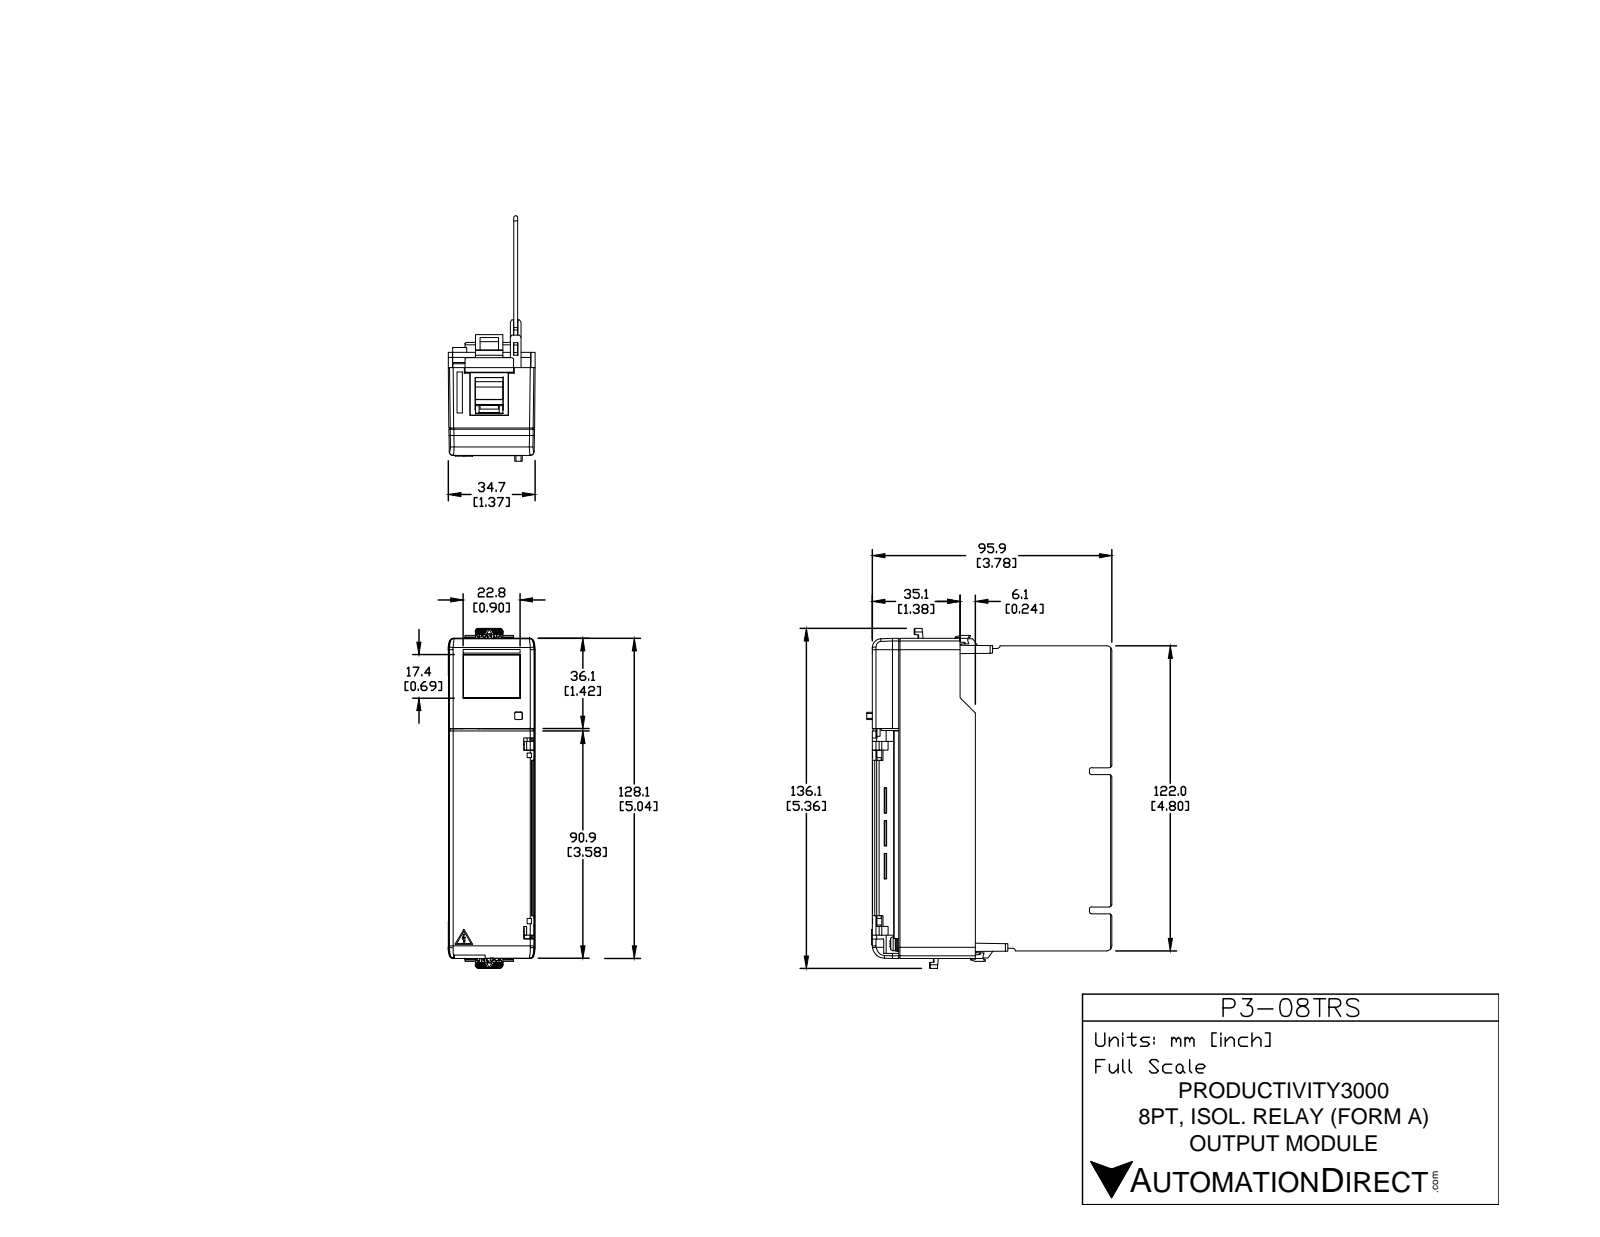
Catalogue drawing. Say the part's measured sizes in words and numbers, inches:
The part is named "P3-08TRS". Its 3-D file was written by "SolidWorks 2009 (CONFIG_CONTROL_DESIGN)". It is 1 solid with 3804 faces: 2821 planar, 737 cylindrical and 246 other. Overall it measures 5.357 by 3.787 by 1.37 inches. Its volume is 6.184 cubic inches and its surface area 116.9 square inches. Round holes: 22 of diameter 0.126, 2 of diameter 0.197, 1 of diameter 0.071. Round bosses or shafts: 22 of diameter 0.217, 22 of diameter 0.118, 20 of diameter 0.094, 2 of diameter 0.22, 2 of diameter 0.087, 2 of diameter 0.079, 1 of diameter 0.059. Partial cylindrical surfaces (rounded edges, fillets, slot ends): 91 of radius 0.02, 33 of radius 0.039, 29 of radius 0.012, 22 of radius 0.066, 13 of radius 0.059, 6 of radius 0.079, 5 of radius 0.008, 4 of radius 0.004. The main face-to-face distances are 0.063, 0.067, 1.111, 1.044, 1.282, 0.874, 0.087, 0.311, 0.268, 0.209. The hole center spacings are 0.342, 0.3, 0.545, 0.6, 0.811, 0.9, 1.094, 1.2.
